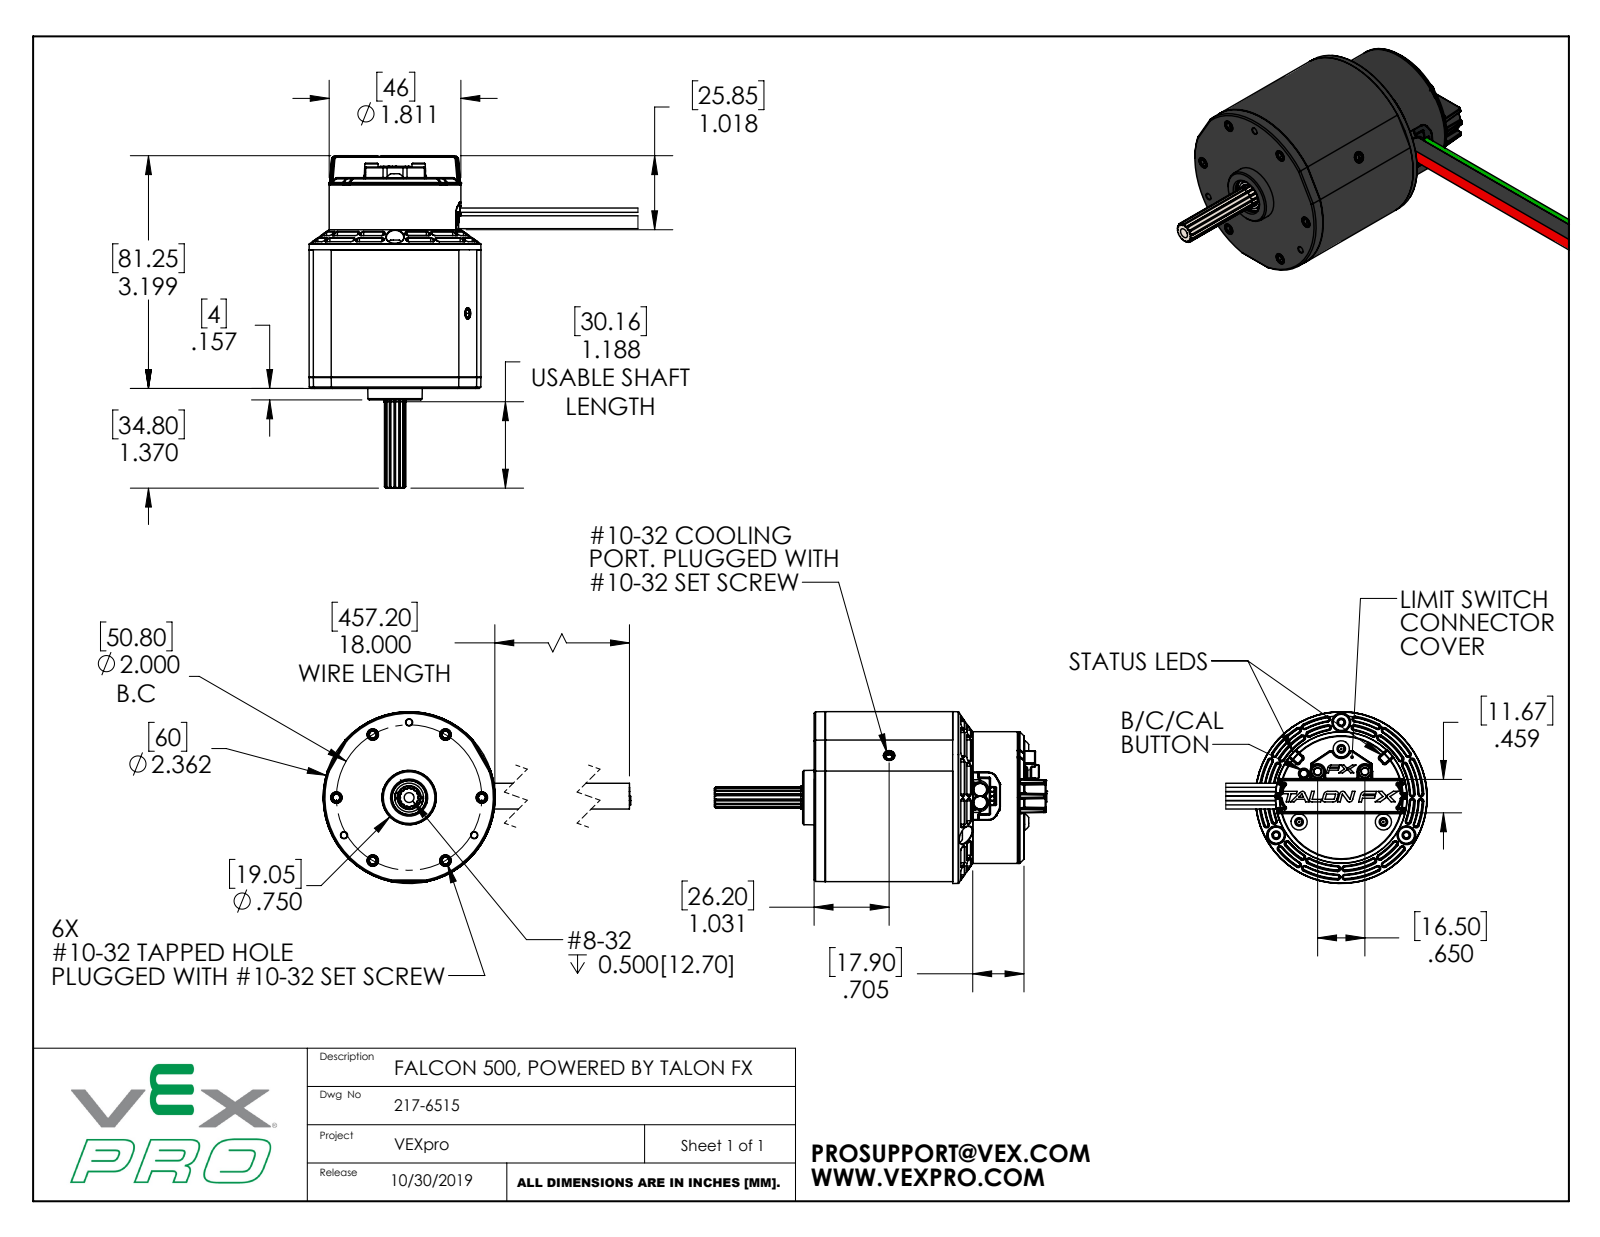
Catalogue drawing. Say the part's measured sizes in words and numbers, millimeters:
The part is named "M3 BHTS, Grade 8 Steel Rev1_SBTM3-50MMZB; 217-6515-202 Rev6; 217-6515-001 Rev6; am-6515 Falcon 500 Brushless Motor with Long Shaft (+8 more)". Its 3-D file was written by "SolidWorks 2019 (AUTOMOTIVE_DESIGN)". It is 42 solids with 5231 faces: 1848 planar, 921 cylindrical and 2462 other. Overall it measures 116.05 by 60 by 60 millimeters. Its volume is 29 057 cubic millimeters and its surface area 60 727 square millimeters. Round holes: 7 of diameter 4.04, 5 of diameter 2.05, 5 of diameter 2.9, 5 of diameter 4.75, 3 of diameter 2.5, 3 of diameter 3.2, 2 of diameter 2.26, 2 of diameter 2.95, 1 of diameter 3, 1 of diameter 3.45, 1 of diameter 4.57, 1 of diameter 5. Round bosses or shafts: 7 of diameter 4.83, 7 of diameter 4.5, 6 of diameter 3, 5 of diameter 2.5, 5 of diameter 1.02, 4 of diameter 1.5, 3 of diameter 5.7, 3 of diameter 5.69. Partial cylindrical surfaces (rounded edges, fillets, slot ends): 192 of radius 0.2, 81 of radius 0.3, 44 of radius 0.5, 36 of radius 0.15, 36 of radius 0.8, 9 of radius 0.1, 8 of radius 3, 5 of radius 0.25. The main face-to-face distances are 2, 7.4, 46.4, 65, 4, 2.38, 57.6, 59.98, 67.38, 44.4. The hole center spacings are 25.4, 13.4, 13.65, 30.56, 49.89, 8.23, 13.32, 25.39.
